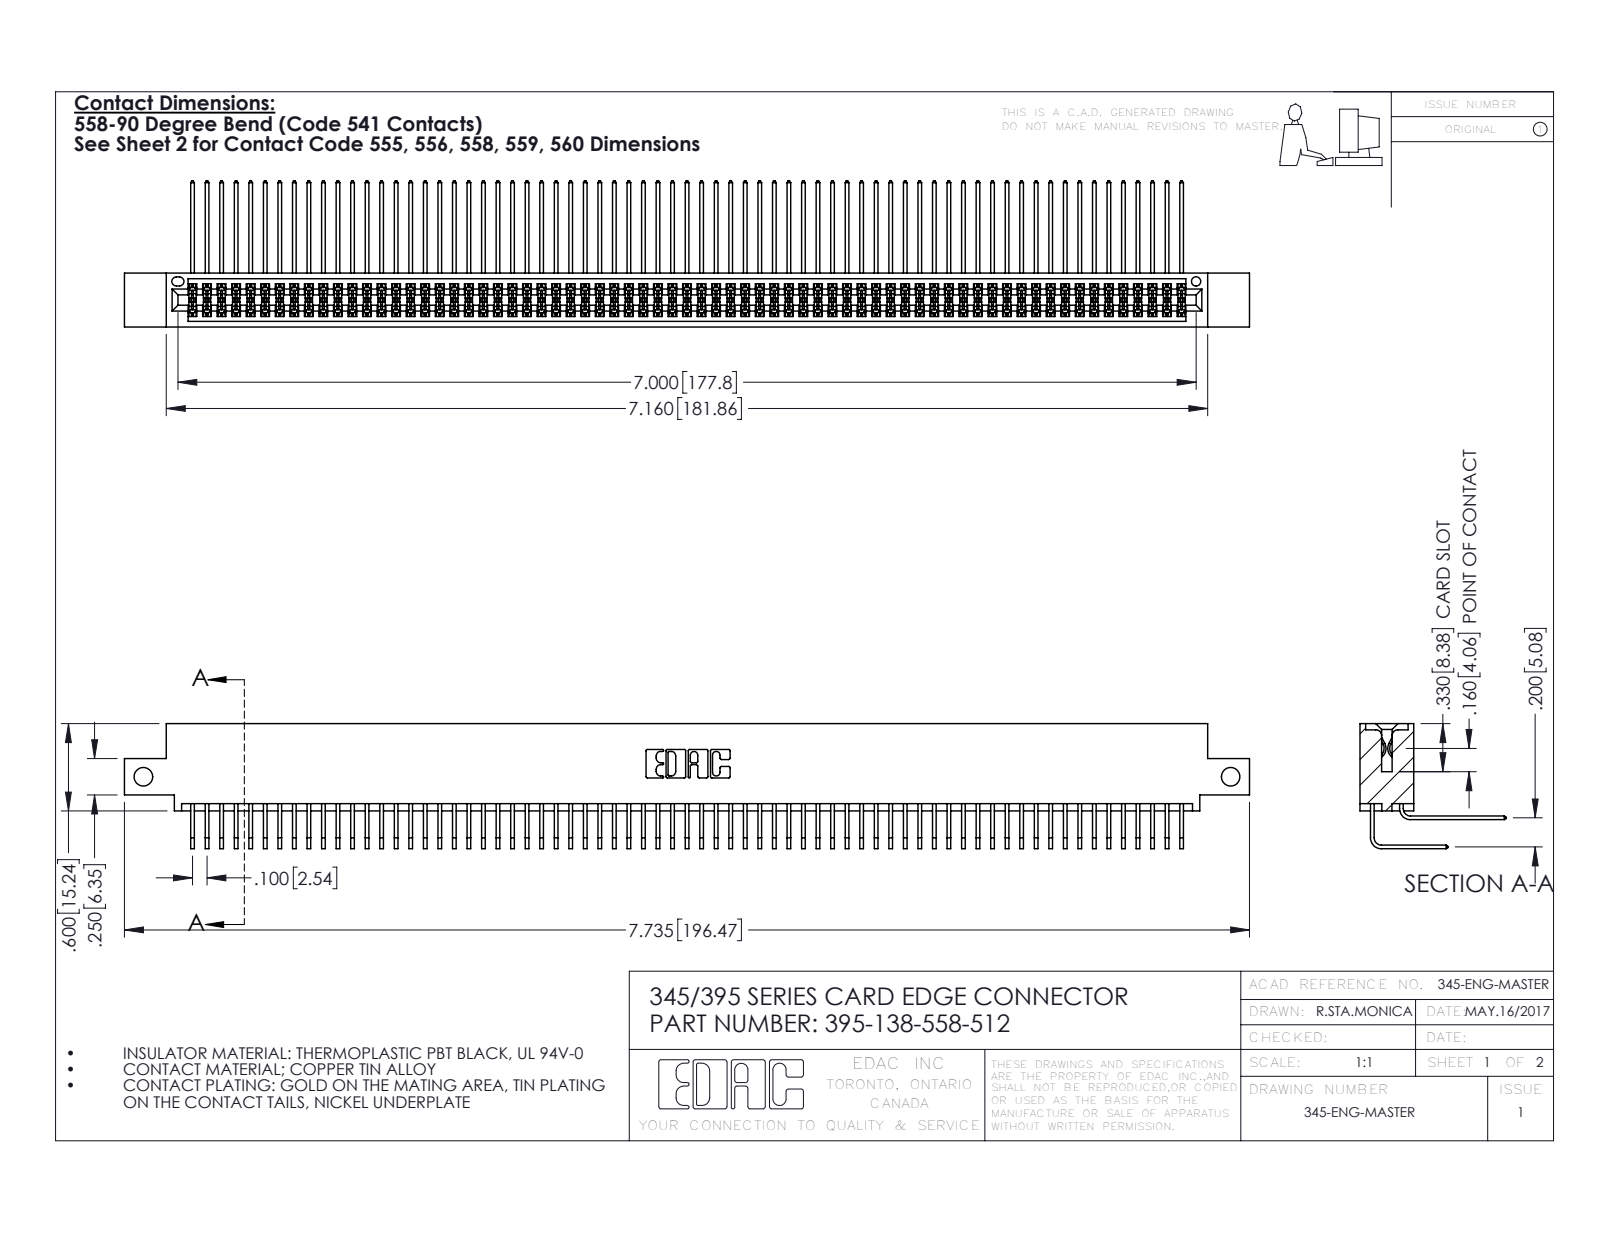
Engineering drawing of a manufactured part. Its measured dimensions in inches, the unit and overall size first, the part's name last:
Units: inches
Overall size (bounding box): 7.735 × 1.005 × 0.859
Round holes (diameter × count): ⌀0.128 ×2, ⌀0.064 ×1
Partial cylindrical surfaces — rounded edges, fillets, slot ends (radius × count): R0.006 ×275, R0.01 ×22, R0.007 ×6, R0.031 ×6, R0.026 ×3, R0.014 ×2, R0.019 ×2, R0.022 ×2
Main face-to-face distances: 0.072, 0.298, 0.2, 0.37, 0.098, 0.272, 0.025, 0.225, 0.025, 0.175
Hole centre spacings: 7.475
Volume: 1.219 in³ · Surface area: 52.3 in²
Bodies: 139 solids, 7306 faces (4914 planar, 2392 cylindrical, 0 other)
Part name (STEP PRODUCT): 345-292-001_558 Tail - 2; 345-292-001_558 559 Tail - 1; 345 Part_0.110 Offset - Side Mount; 395-138-558-512
STEP written by: SolidWorks 2016 (CONFIG_CONTROL_DESIGN)
